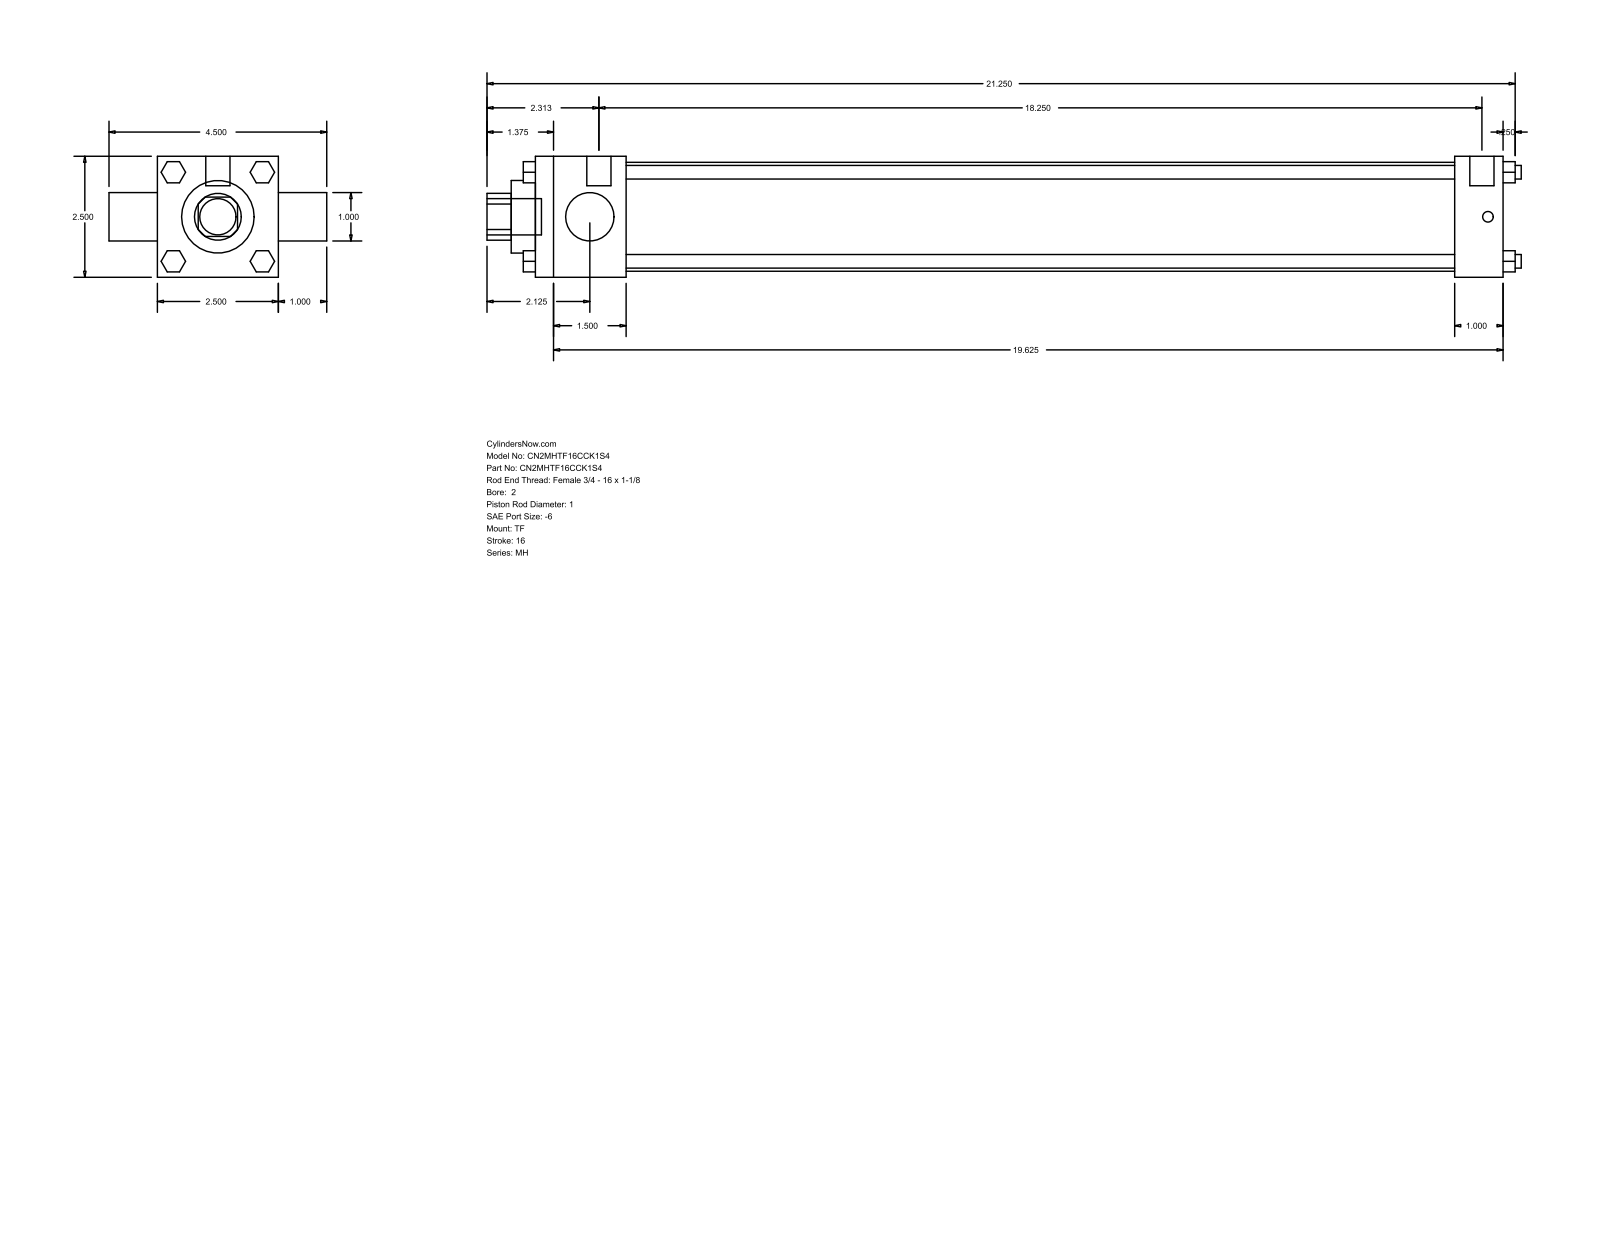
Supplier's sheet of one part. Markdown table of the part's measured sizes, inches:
| quantity | value |
| --- | --- |
| part name | MH_TF__0200_1 |
| STEP written by | GSSL Pune (CONFIG_CONTROL_DESIGN) |
| units | inches |
| bodies | 0 solids, 120 faces (92 planar, 28 cylindrical, 0 other) |
| overall size | 21.375 × 4.5 × 2.5 |
| round holes (diameter × count) | 1 × 2, 1.5 × 1, 2.25 × 1 |
| round bosses / shafts (diameter × count) | 0.281 × 4, 0.219 × 3, 0.5 × 2, 0.75 × 1 |
| partial cylindrical surfaces (radius × count) | 0.484 × 1 |
| main face-to-face distances | 2.5, 20, 1, 1.875, 19, 17.125, 18.125, 3.5, 20.5, 0.25 |
